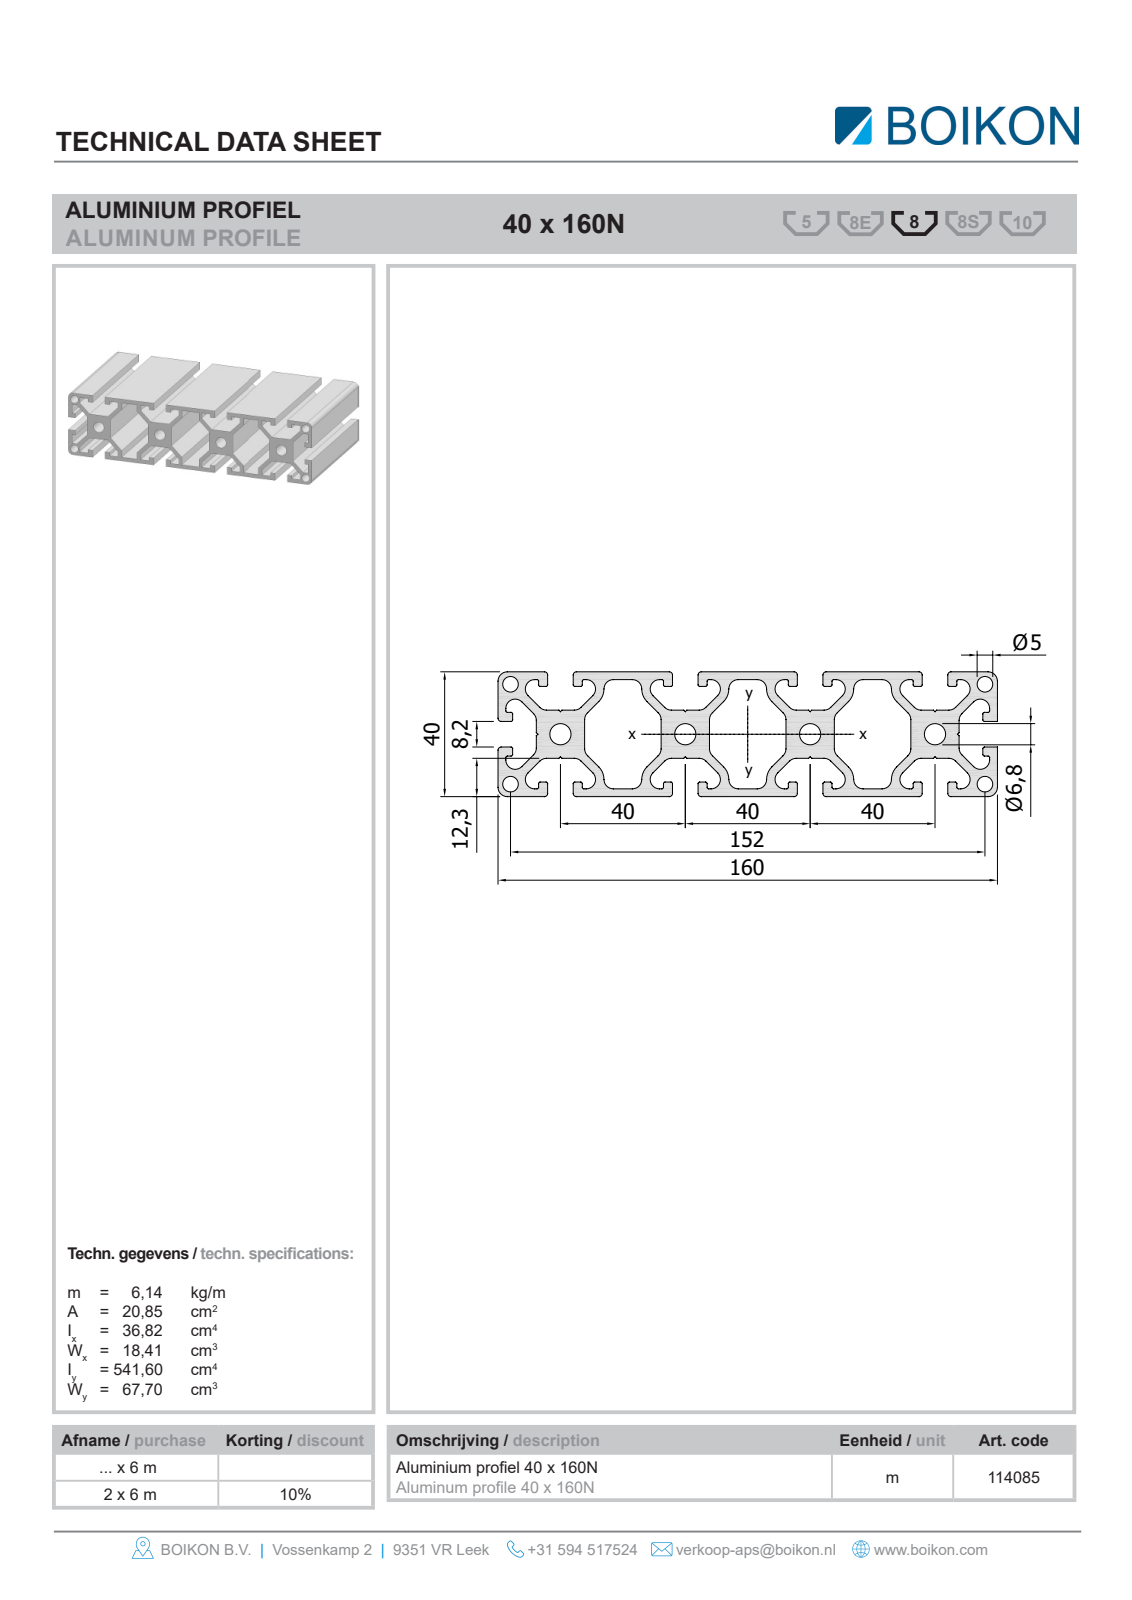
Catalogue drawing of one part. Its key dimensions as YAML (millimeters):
part_name: "Root; 11408540x160NBOIKON0"
step_written_by: "HiCAD 2013 1802.4 Build 509 (AUTOMOTIVE_DESIGN)"
units: millimeters
bodies: {solids: 1, faces: 194, planar: 182, cylindrical: 12, other: 0}
overall_size: [1000, 160, 40]
volume: 2119000
surface_area: 1449000
round_holes:
  - {diameter: 5, count: 4}
  - {diameter: 6.8, count: 4}
partial_cylinders:
  - {radius: 3, count: 4}
face_to_face_distances: [2.4, 40, 28.28, 56.56, 37.6, 12.3, 27.7, 9.9, 25.3, 25.88]
hole_center_spacings: [22.63, 58.24, 97.32, 136.94, 40, 32, 80, 152]
